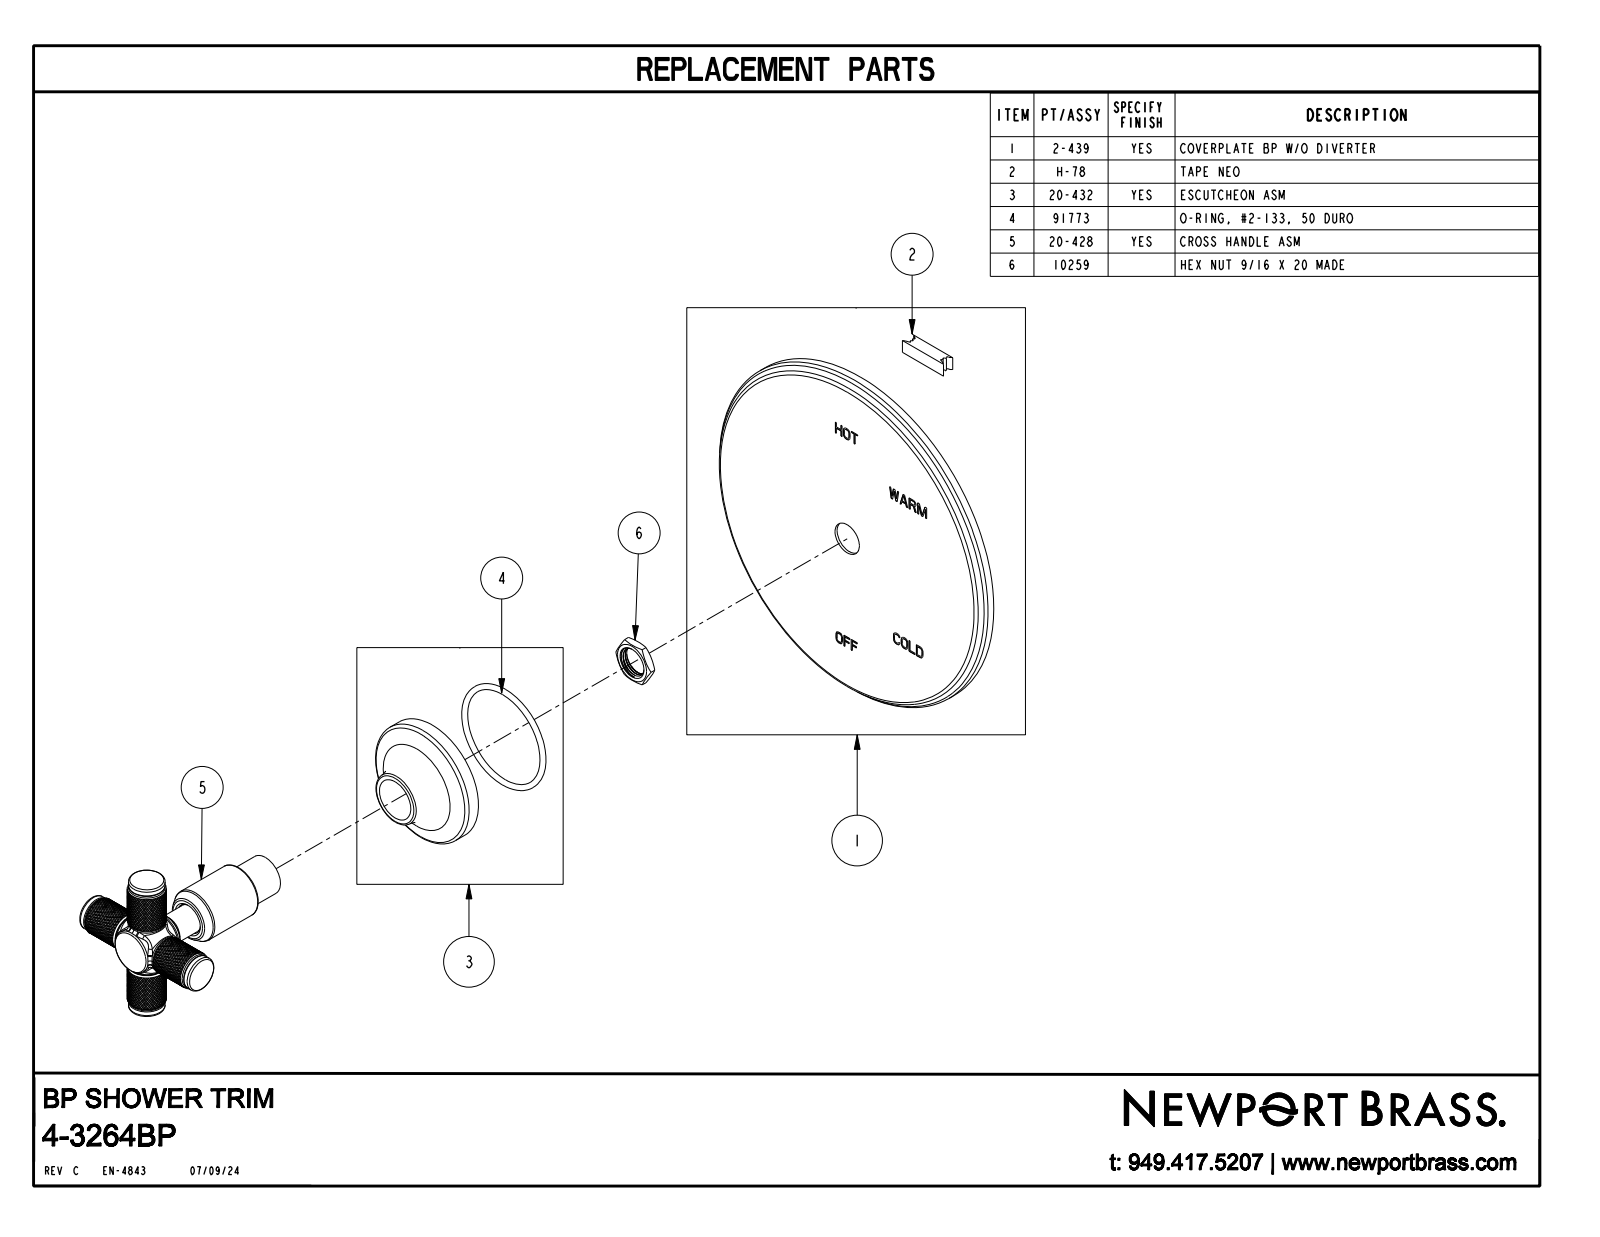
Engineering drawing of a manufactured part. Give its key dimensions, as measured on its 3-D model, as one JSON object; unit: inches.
{"part_name": "11117; H-78; 2-439_ASM; 13125 (+8 more)", "step_written_by": "CREO PARAMETRIC BY PTC INC, 2018400 (CONFIG_CONTROL_DESIGN)", "units": "inches", "bodies": {"solids": 17, "faces": 12103, "planar": 578, "cylindrical": 2643, "other": 8882}, "overall_size": [6.5, 6.5, 3.967], "volume_in3": 5.422, "surface_area_in2": 312.3, "round_holes": [[0.25, 2], [0.403, 2], [0.47, 2], [0.11, 1], [0.14, 1], [0.275, 1], [0.358, 1], [0.36, 1], [0.375, 1], [0.383, 1], [0.397, 1], [0.4, 1]], "round_bosses_or_shafts": [[0.67, 2], [0.63, 2], [0.433, 2], [0.37, 2], [6.5, 1], [2.25, 1], [1.812, 1], [0.965, 1]], "partial_cylinders_radius": [[0.01, 6], [0.042, 6], [0.072, 1], [0.137, 1], [0.149, 1], [0.169, 1], [0.394, 1]], "face_to_face_distances": [0.05, 0.25, 0.3, 0.465, 0.263, 0.313, 0.563, 0.085, 1.213, 0.165]}
